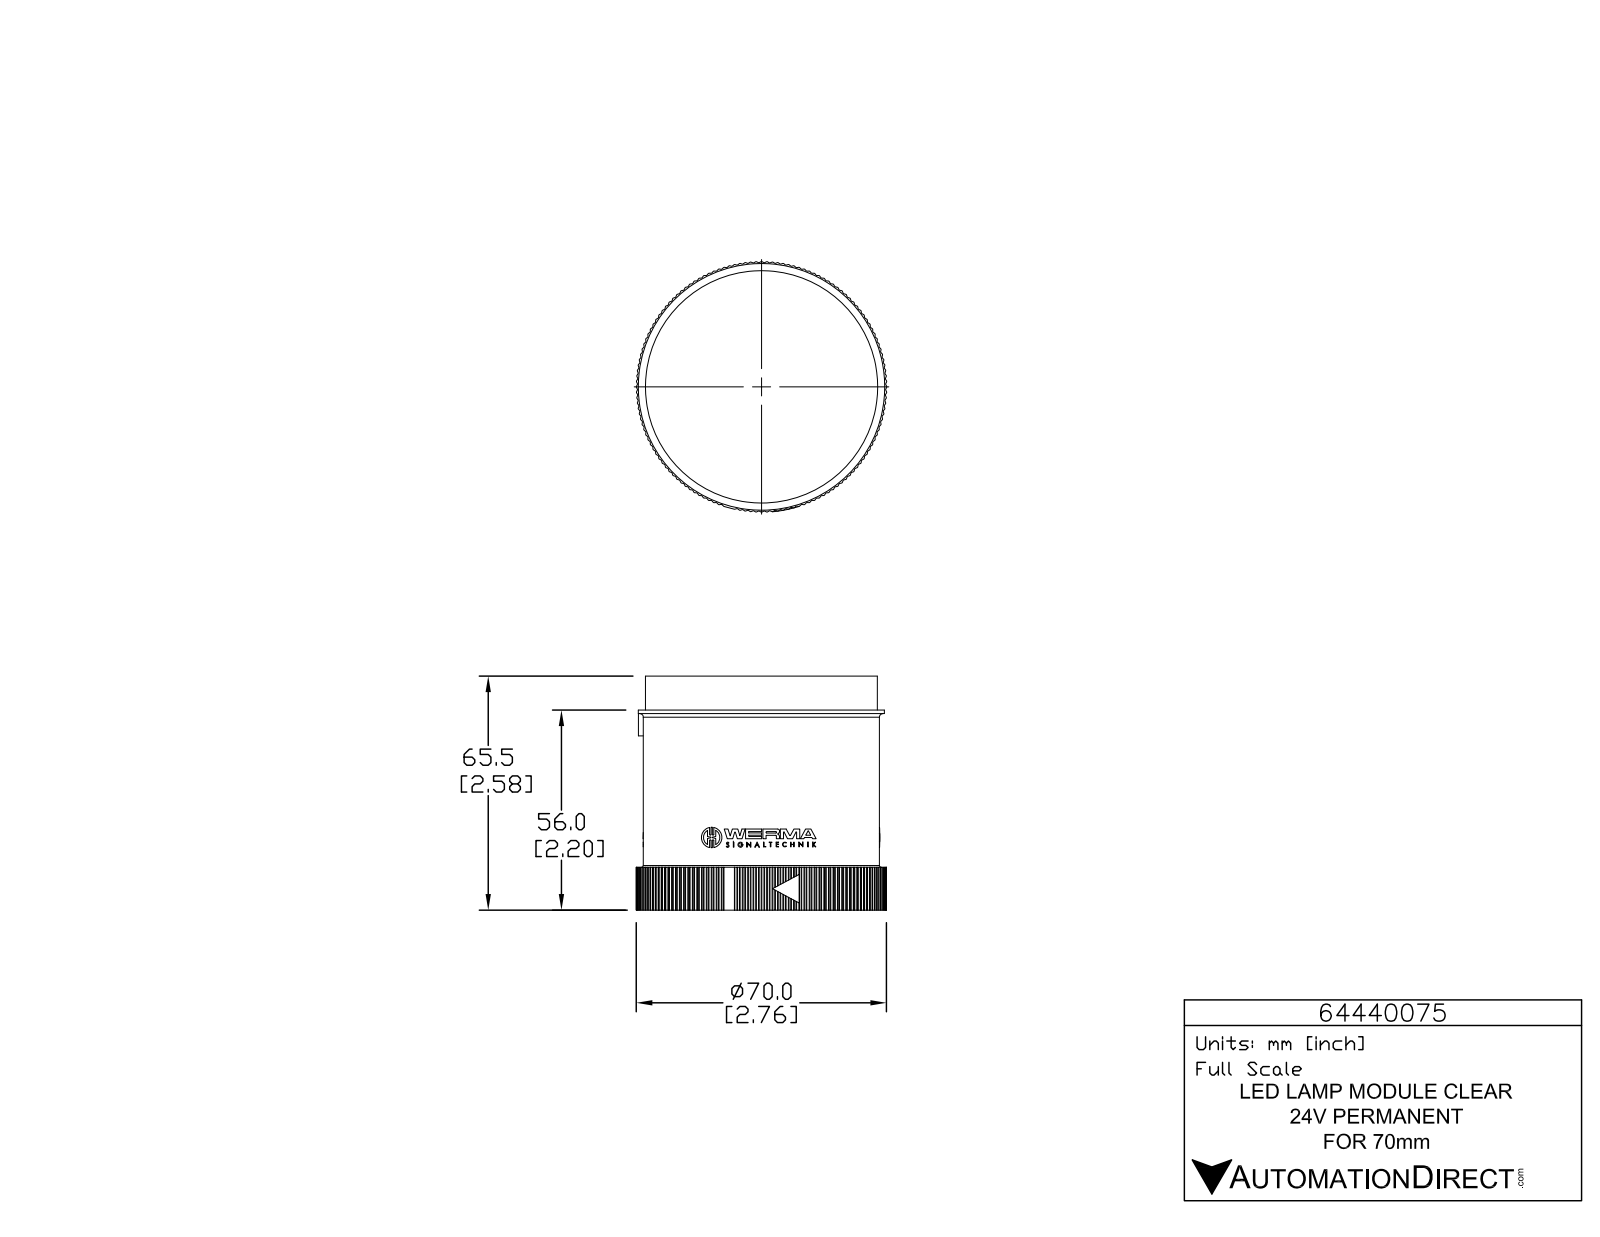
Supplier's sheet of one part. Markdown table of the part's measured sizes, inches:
| quantity | value |
| --- | --- |
| part name | 64440075 |
| STEP written by | SolidWorks 2015 (AUTOMOTIVE_DESIGN) |
| units | inches |
| bodies | 1 solid, 1400 faces (832 planar, 563 cylindrical, 5 other) |
| overall size | 2.762 × 2.762 × 2.579 |
| volume | 12.02 in³ |
| surface area | 37.48 in² |
| round holes (diameter × count) | 0.039 × 3, 2.575 × 1 |
| round bosses / shafts (diameter × count) | 0.226 × 3, 0.056 × 3, 2.717 × 1, 2.606 × 1, 2.559 × 1 |
| partial cylindrical surfaces (radius × count) | 0.008 × 285, 0.008 × 6, 0.008 × 6, 0.008 × 6, 0.131 × 6, 0.004 × 3, 0.005 × 3, 0.008 × 3 |
| main face-to-face distances | 2.201, 2.451, 0.378, 2.579, 2.205, 1.827, 0.374, 2.452, 0.472, 0.094 |
